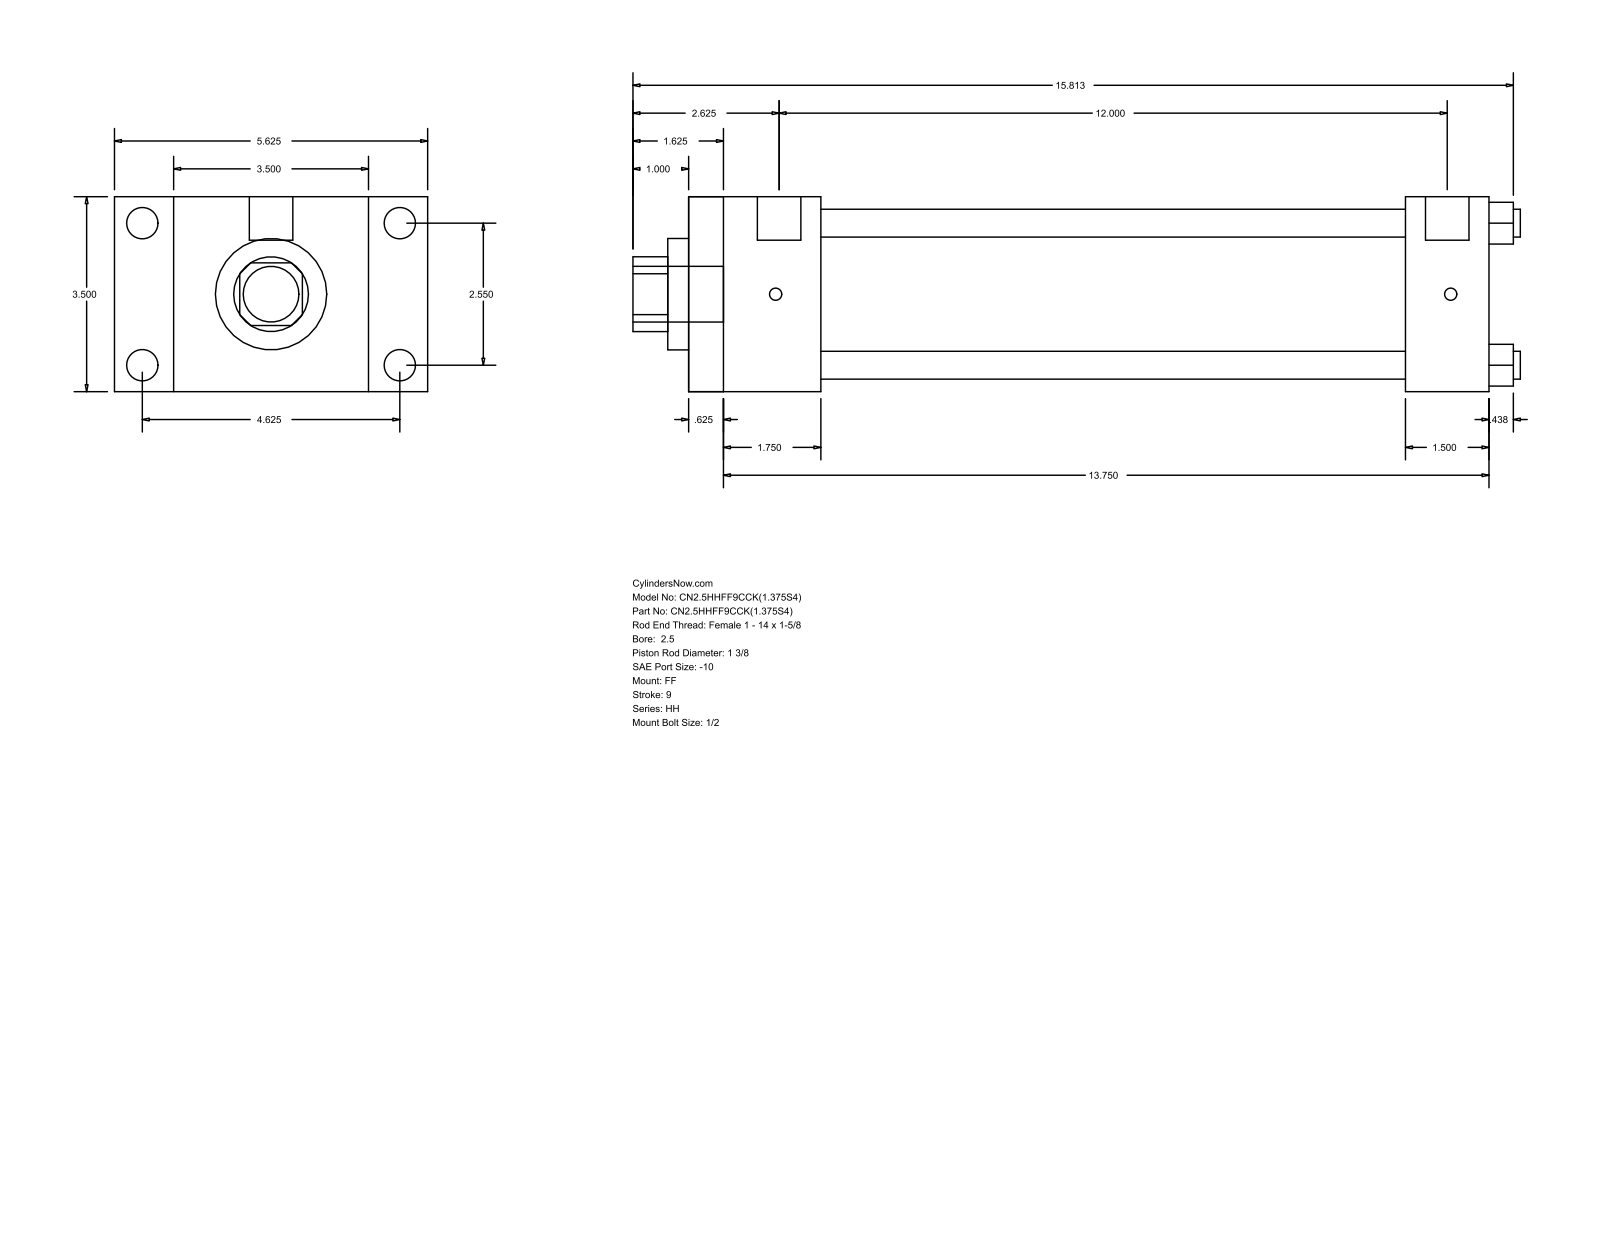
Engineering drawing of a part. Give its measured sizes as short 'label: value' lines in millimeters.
name: HH_FF__0250_1.375
written by: GSSL Pune (CONFIG_CONTROL_DESIGN)
unit: mm
bodies: 0 solids, 92 faces (64 planar, 28 cylindrical, 0 other)
size: 404.81 × 142.88 × 88.9
holes: 4× ⌀12.7, 1× ⌀34.92, 1× ⌀50.8, 1× ⌀73.03
bosses: 4× ⌀14.3, 4× ⌀5.56, 2× ⌀19.84, 1× ⌀25.4
rounds: 1× R17.06
face distances: 88.9, 365.12, 15.87, 349.25, 60.32, 44.45, 304.8, 327.03, 311.16, 266.71
hole spacings: 45.79, 64.76, 91.58
